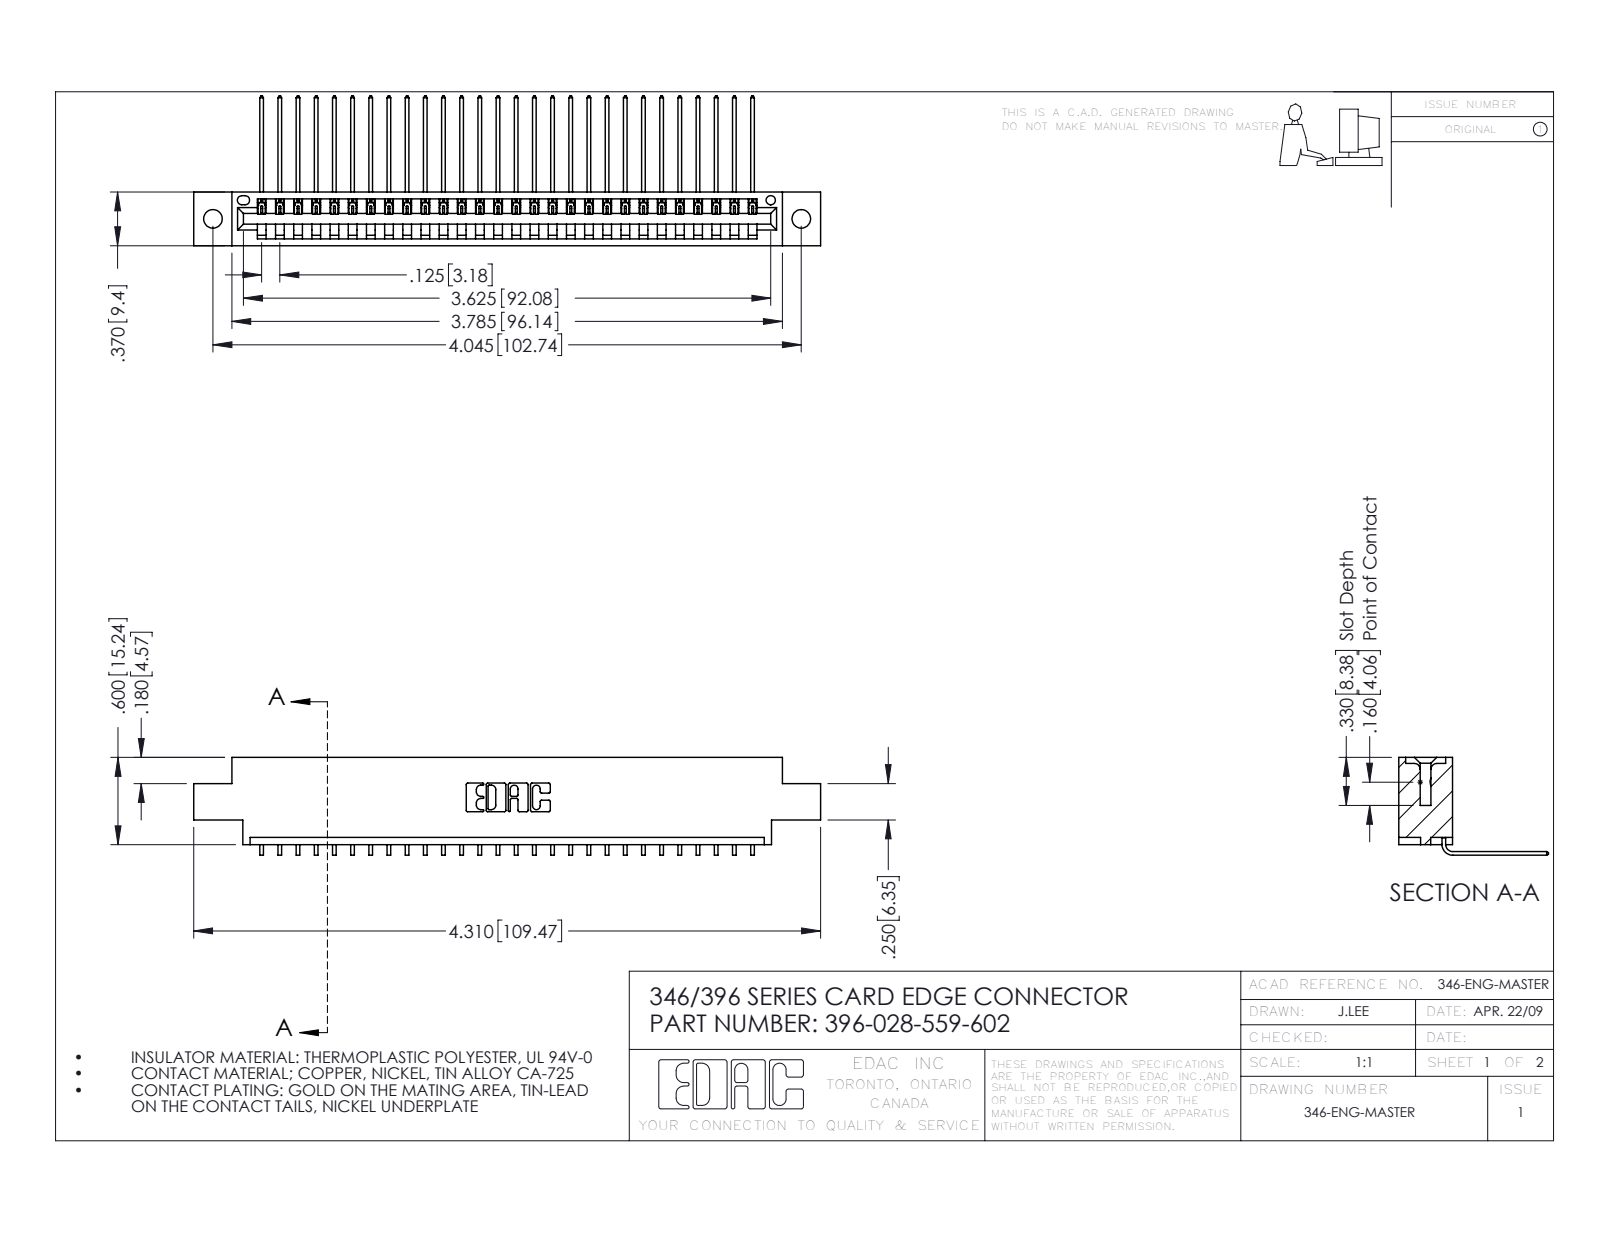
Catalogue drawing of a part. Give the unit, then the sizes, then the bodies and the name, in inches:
Units: inches
Overall size (bounding box): 4.31 × 1.03 × 0.673
Round holes (diameter × count): ⌀0.128 ×2, ⌀0.064 ×1
Partial cylindrical surfaces — rounded edges, fillets, slot ends (radius × count): R0.006 ×56, R0.01 ×22, R0.007 ×6, R0.031 ×6, R0.026 ×3, R0.031 ×2, R0.04 ×2, R0.014 ×1
Main face-to-face distances: 0.048, 0.322, 0.37, 0.25, 0.025, 0.072, 0.148, 0.222, 0.1, 0.174
Hole centre spacings: 0.246, 3.837, 4.045
Volume: 0.628 in³ · Surface area: 20.38 in²
Bodies: 29 solids, 1806 faces (1256 planar, 550 cylindrical, 0 other)
Part name (STEP PRODUCT): 346 Part_0.170 Offset - 0.128 Dia; 396-028-559-602; 345-292-001_558 559 Tail - 1
STEP written by: SolidWorks 2016 (CONFIG_CONTROL_DESIGN)
